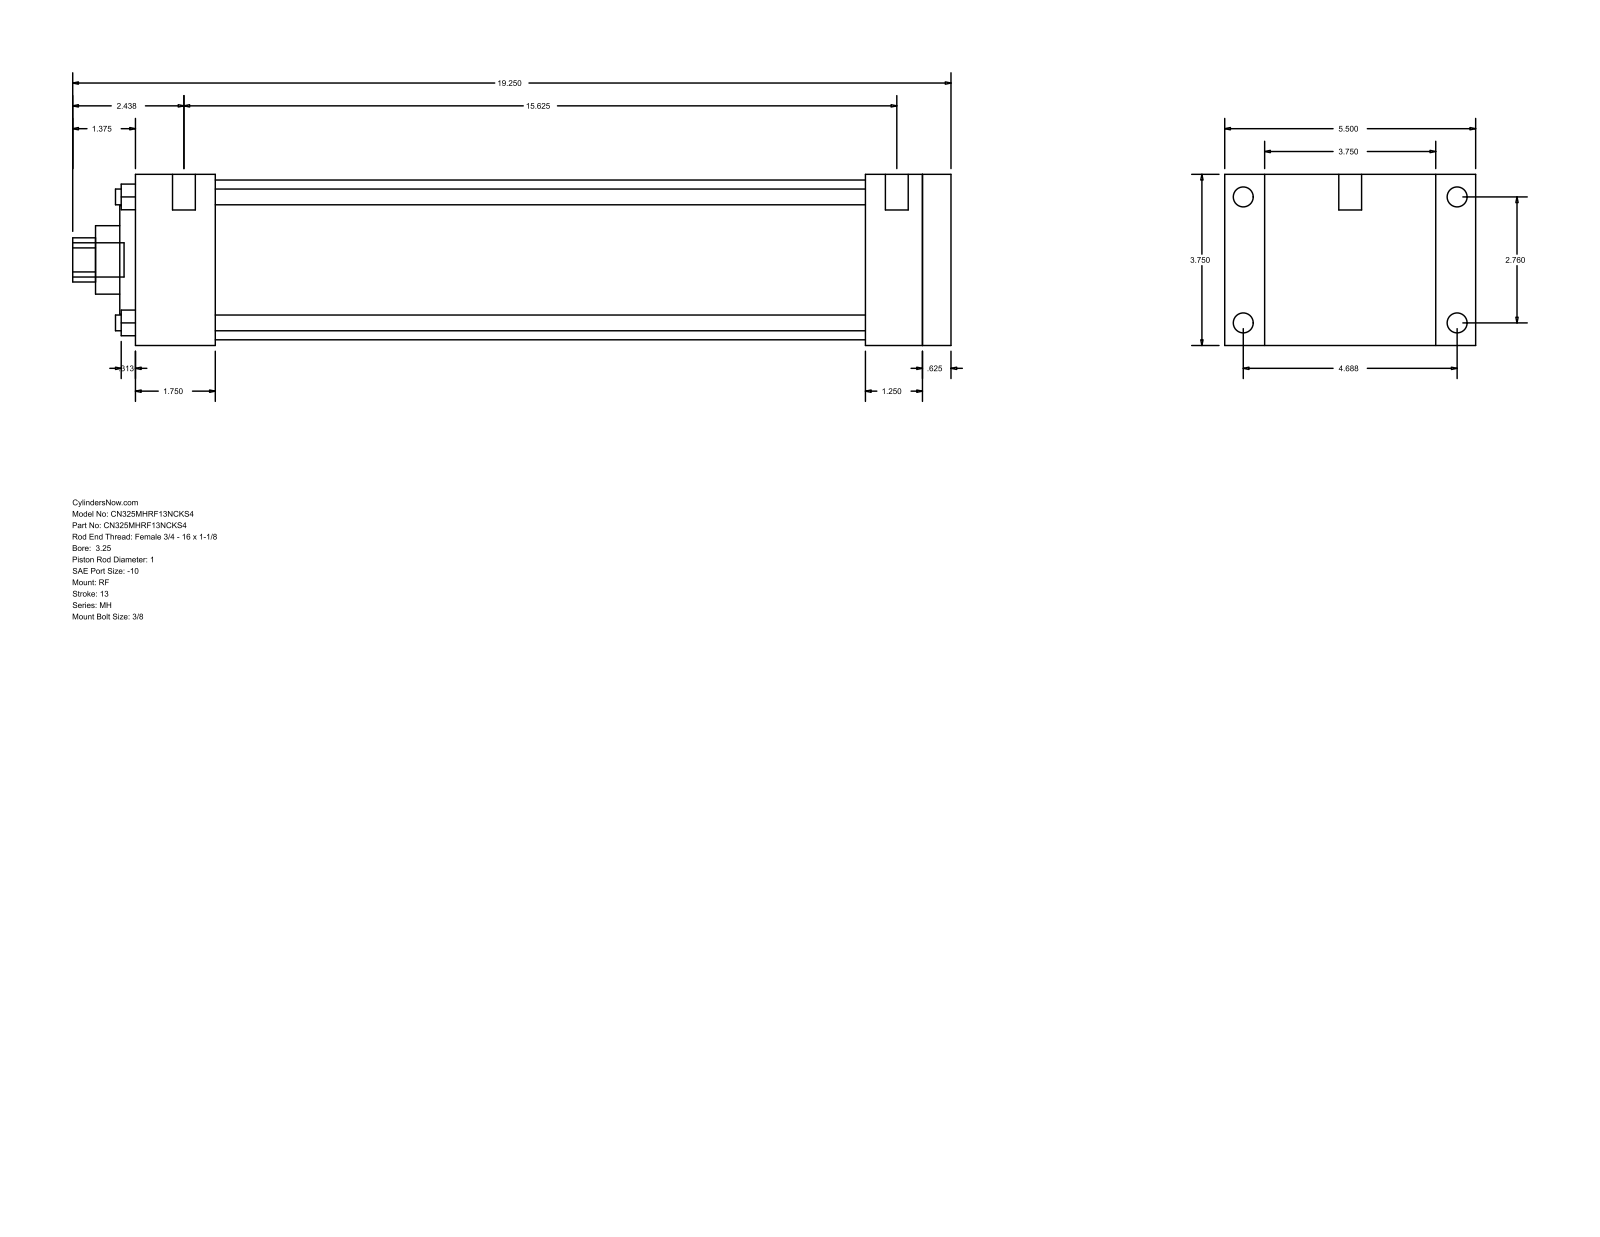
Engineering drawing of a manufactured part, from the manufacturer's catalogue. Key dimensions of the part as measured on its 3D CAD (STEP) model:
Part name (STEP PRODUCT): MH_RF__0325_1
STEP written by: GSSL Pune (CONFIG_CONTROL_DESIGN)
Units: millimetres
Bodies: 0 solids, 94 faces (65 planar, 29 cylindrical, 0 other)
Overall size (bounding box): 488.95 × 139.7 × 95.25
Round holes (diameter × count): ⌀8.76 ×4, ⌀25.4 ×1, ⌀38.1 ×1, ⌀60.33 ×1, ⌀88.9 ×1
Round bosses / shafts (diameter × count): ⌀11.13 ×4, ⌀5.56 ×4, ⌀12.7 ×2, ⌀19.05 ×1
Partial cylindrical surfaces — rounded edges, fillets, slot ends (radius × count): R12.29 ×1
Main face-to-face distances: 95.24, 454.03, 438.15, 15.88, 22.23, 117.47, 44.46, 393.69, 409.57, 406.4
Hole centre spacings: 49.57, 70.1, 99.14
